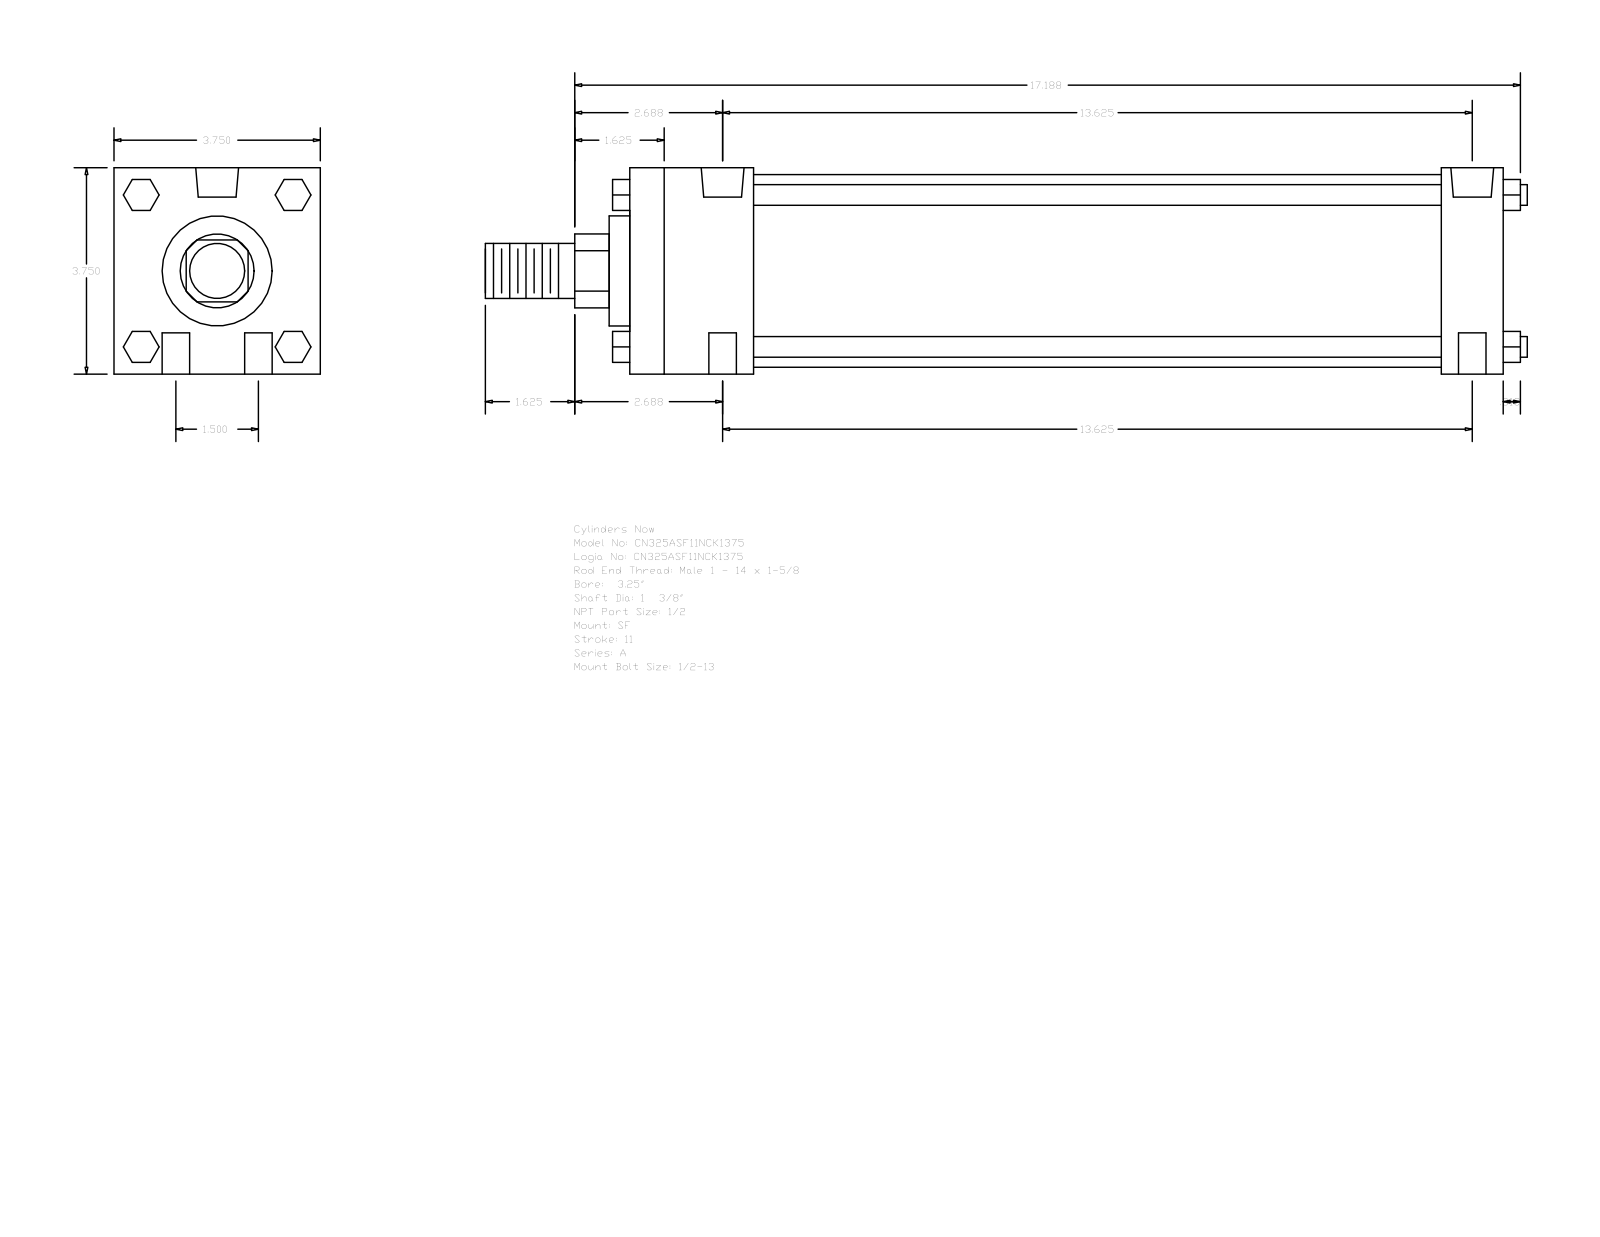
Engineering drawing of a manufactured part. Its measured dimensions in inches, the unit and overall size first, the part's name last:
Units: inches
Overall size (bounding box): 18.937 × 3.75 × 3.75
Round holes (diameter × count): ⌀0.5 ×4, ⌀0.344 ×2, ⌀0.778 ×2
Round bosses / shafts (diameter × count): ⌀0.375 ×4, ⌀3.5 ×1, ⌀2 ×1, ⌀1.375 ×1, ⌀1 ×1
Partial cylindrical surfaces — rounded edges, fillets, slot ends (radius × count): R0.672 ×1
Main face-to-face distances: 3.75, 15.875, 2.25, 14.75, 1.125, 12.5, 13.625, 2.625, 0.375, 15.125
Hole centre spacings: 0.75, 13.646, 13.625, 1.5, 13.707, 13.375
Bodies: 0 solids, 124 faces (94 planar, 30 cylindrical, 0 other)
Part name (STEP PRODUCT): A_SF__0325_1.375
STEP written by: GSSL Pune (CONFIG_CONTROL_DESIGN)
